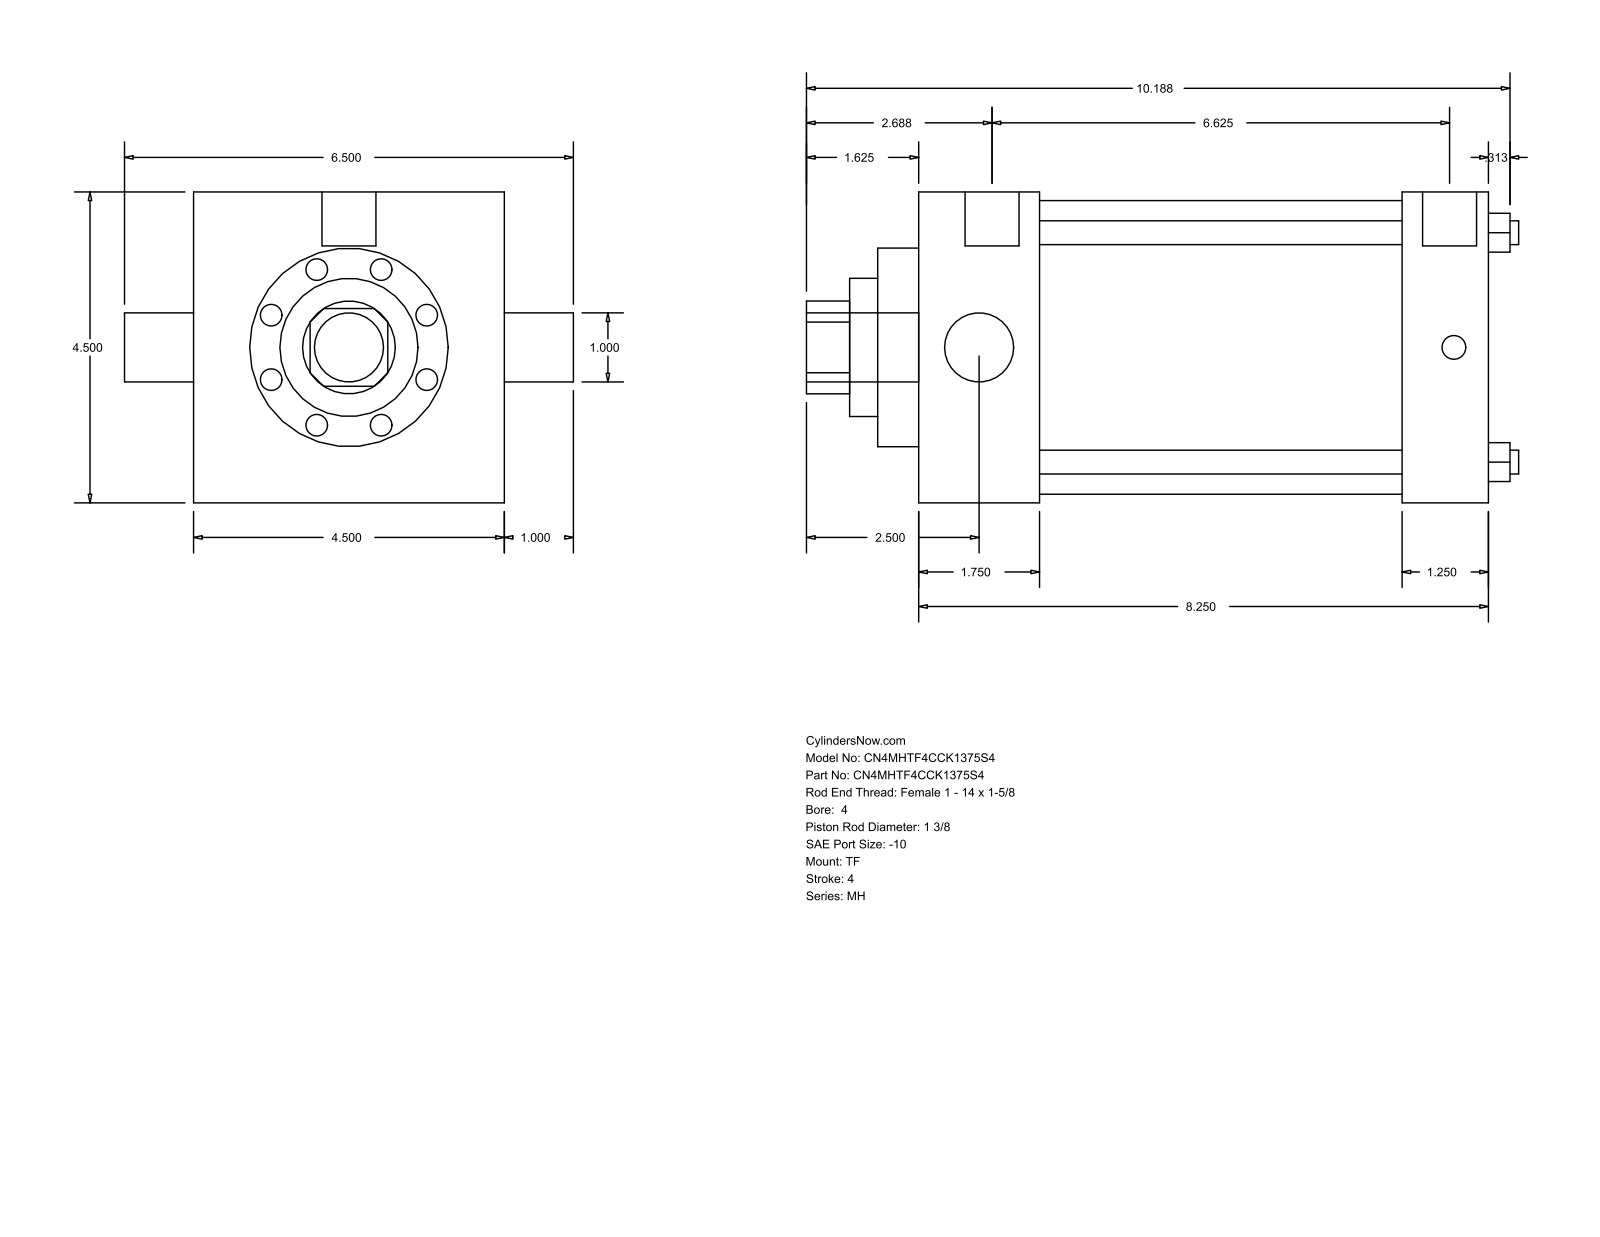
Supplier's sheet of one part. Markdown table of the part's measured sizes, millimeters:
| quantity | value |
| --- | --- |
| part name | MH_TF__0400_1.375 |
| STEP written by | GSSL Pune (CONFIG_CONTROL_DESIGN) |
| units | millimeters |
| bodies | 0 solids, 86 faces (61 planar, 25 cylindrical, 0 other) |
| overall size | 261.94 × 165.1 × 114.3 |
| round holes (diameter × count) | 8.76 × 4, 25.4 × 1, 34.92 × 1, 50.8 × 1, 73.03 × 1, 107.95 × 1 |
| round bosses / shafts (diameter × count) | 8.73 × 3, 19.84 × 2, 25.4 × 1 |
| partial cylindrical surfaces (radius × count) | 17.06 × 1 |
| main face-to-face distances | 114.3, 209.55, 165.1, 44.45, 177.8, 133.35, 31.75, 15.08, 59.53, 192.88 |
| hole center spacings | 59.62, 84.32, 119.25 |
